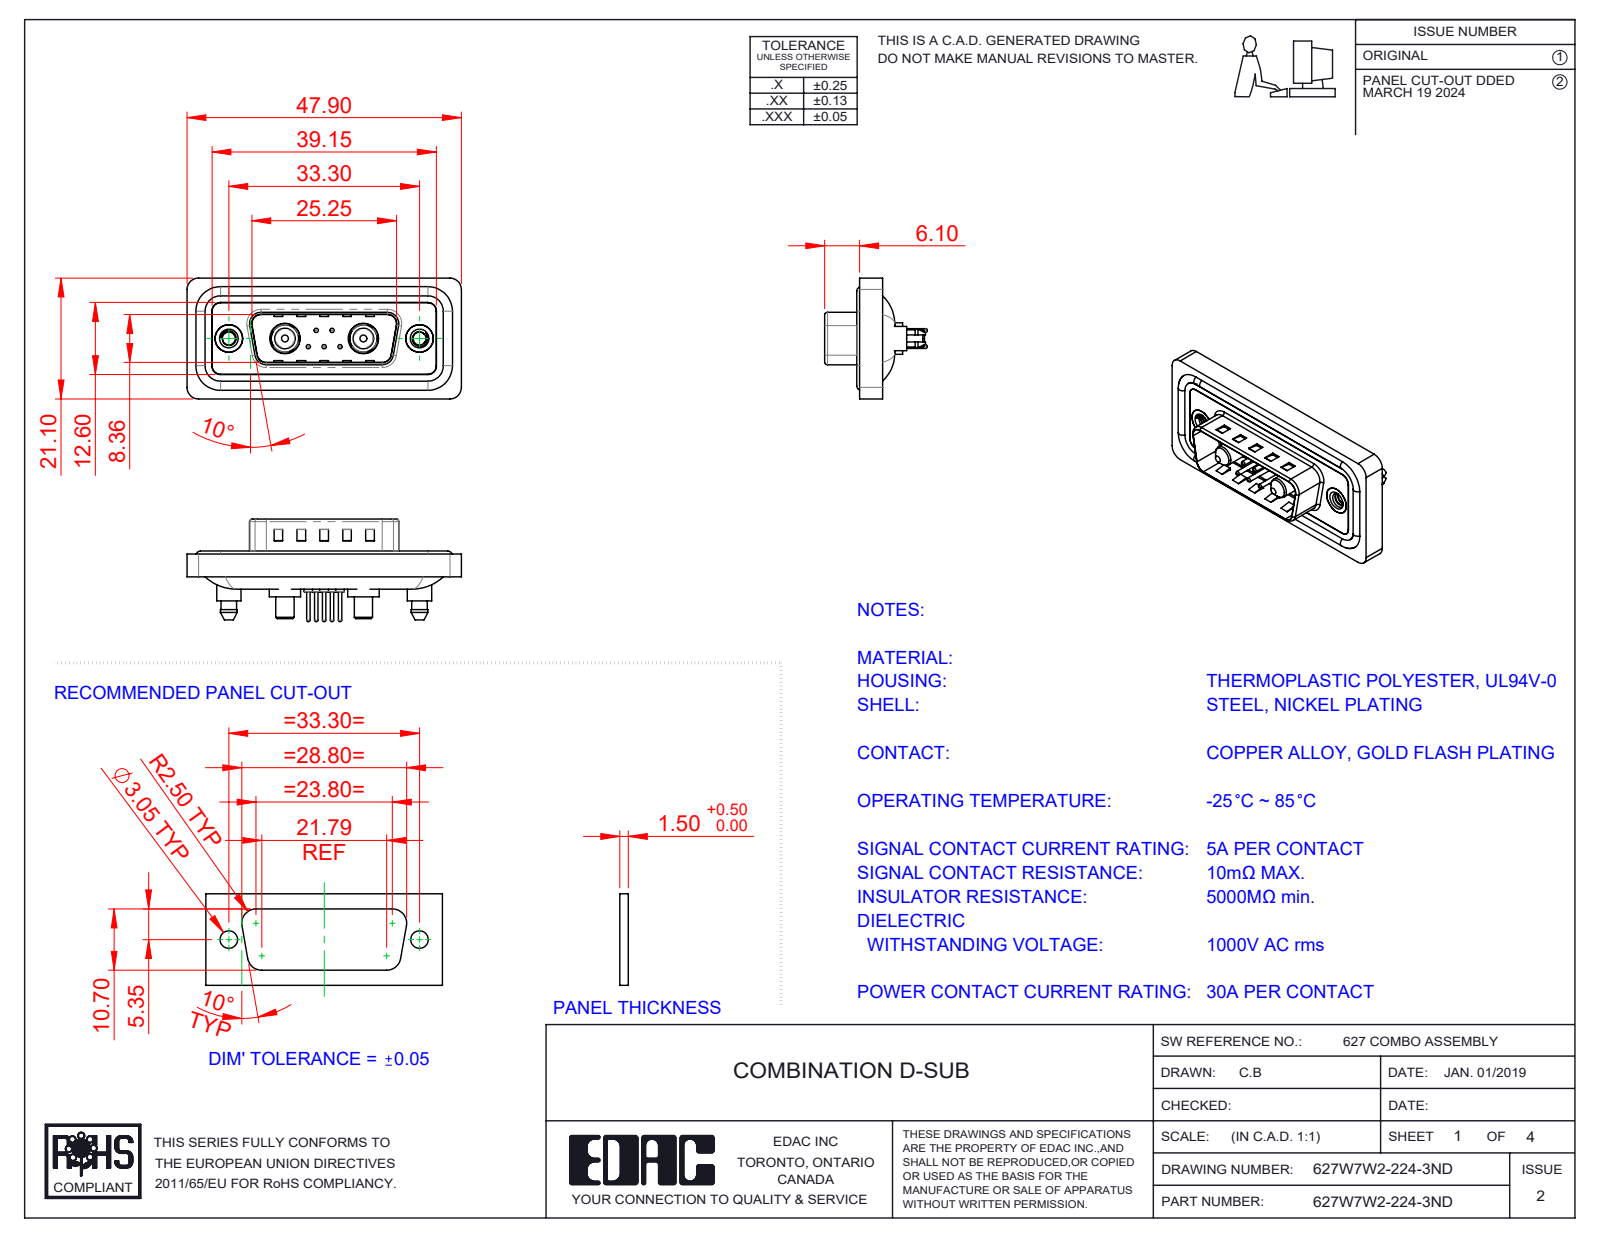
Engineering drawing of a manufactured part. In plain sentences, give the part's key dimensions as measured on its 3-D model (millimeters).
The part is named "627Combo Threaded Boardlock_5; 627Combo Contact Row 2_24; 627Combo Threaded Boardlock_D; 627Combo Housing_7W2 (+6 more)". Its 3-D file was written by "SolidWorks 2023 (CONFIG_CONTROL_DESIGN)". It is 16 solids with 768 faces: 248 planar, 332 cylindrical and 188 other. Overall it measures 47.9 by 21.1 by 17.9 millimeters. Its volume is 5 666 cubic millimeters and its surface area 9 138 square millimeters. Round holes: 5 of diameter 0.75, 5 of diameter 1.6, 5 of diameter 2, 2 of diameter 2.26, 2 of diameter 4, 2 of diameter 4.8, 2 of diameter 4.85, 2 of diameter 5, 2 of diameter 5.3. Round bosses or shafts: 5 of diameter 1.5, 5 of diameter 0.6, 4 of diameter 1.6, 2 of diameter 5.5, 2 of diameter 5.4, 2 of diameter 5.2, 2 of diameter 4.9, 2 of diameter 4.75. Partial cylindrical surfaces (rounded edges, fillets, slot ends): 28 of radius 1.5, 20 of radius 2, 10 of radius 1.6, 8 of radius 0.5, 4 of radius 0.25, 4 of radius 0.6, 4 of radius 0.65, 4 of radius 0.9. The main face-to-face distances are 0.4, 1.1, 1.5, 1.6, 0.5, 3.1, 2.9, 0.7, 4, 0.82. The hole center spacings are 3.16, 2.77, 9.8, 23.5, 4.31, 4.33, 5.03, 5.04.
